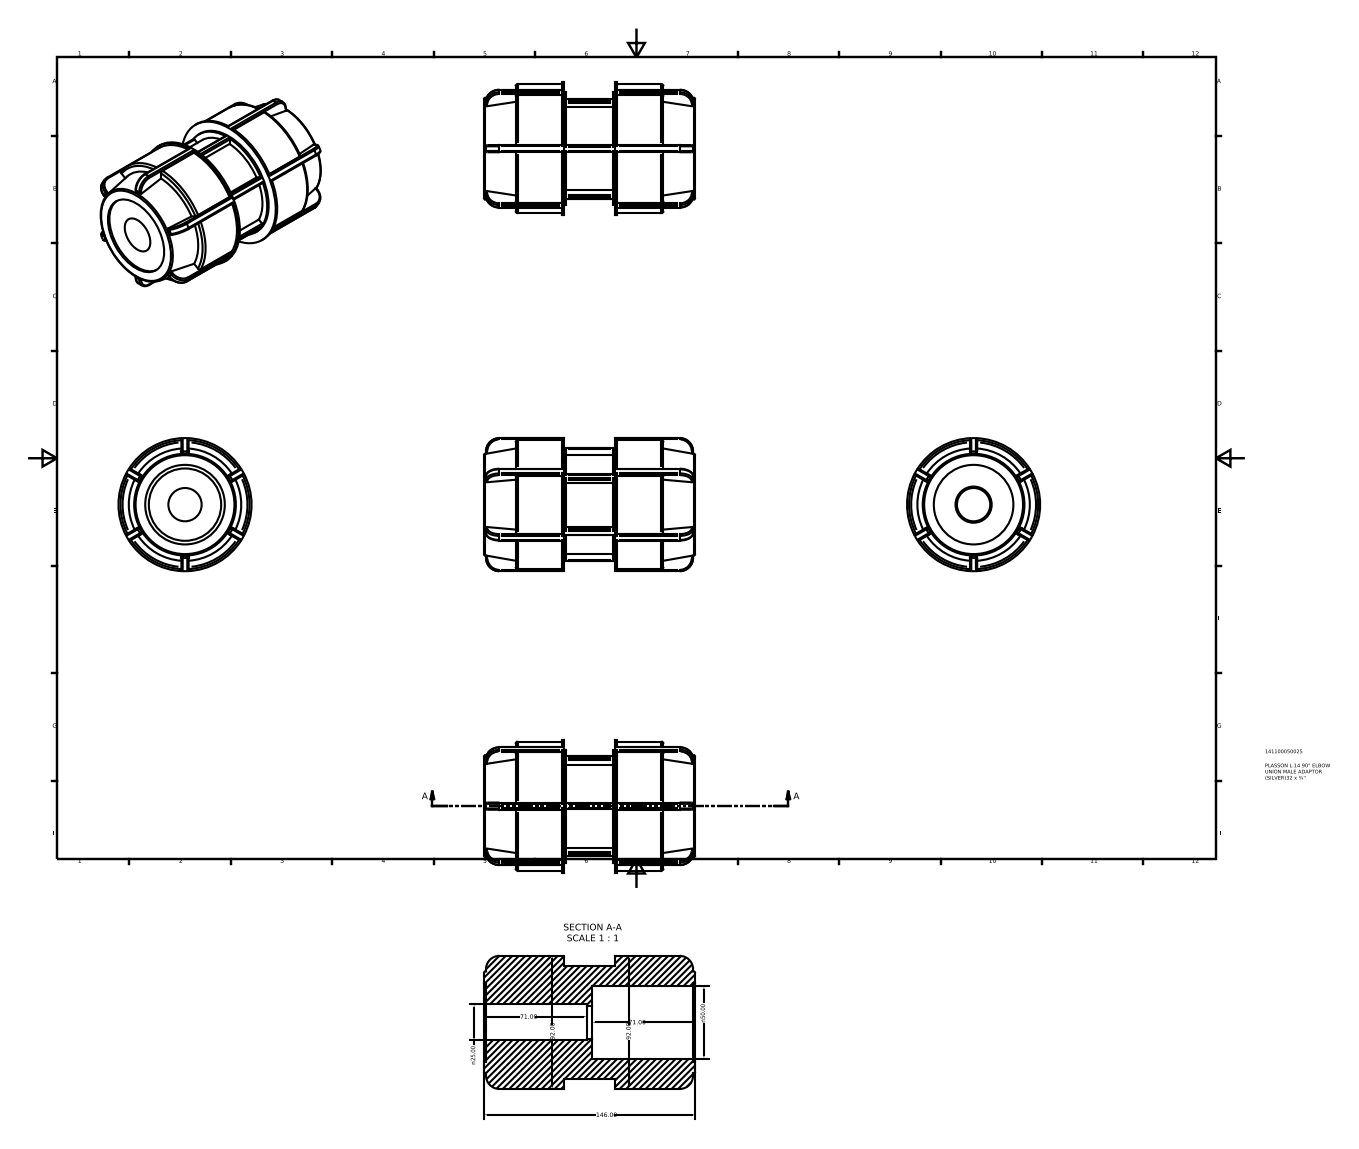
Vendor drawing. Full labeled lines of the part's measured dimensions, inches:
Part name (STEP PRODUCT): 141100050025
STEP written by: Autodesk Inventor 2015 (AUTOMOTIVE_DESIGN)
Units: inches
Bodies: 1 solid, 230 faces (92 planar, 86 cylindrical, 52 other)
Overall size (bounding box): 5.748 × 3.622 × 3.622
Volume: 35.39 in³ · Surface area: 117.7 in²
Round holes (diameter × count): ⌀0.906 ×1, ⌀0.984 ×1, ⌀1.969 ×1, ⌀2.165 ×1
Round bosses / shafts (diameter × count): ⌀3.622 ×1, ⌀3.513 ×1, ⌀3.079 ×1, ⌀2.717 ×1
Partial cylindrical surfaces — rounded edges, fillets, slot ends (radius × count): R0.036 ×36
Main face-to-face distances: 1.38, 0.057, 3.506, 2.184, 1.322, 3.564, 2.127, 0.862, 4.886, 2.702
